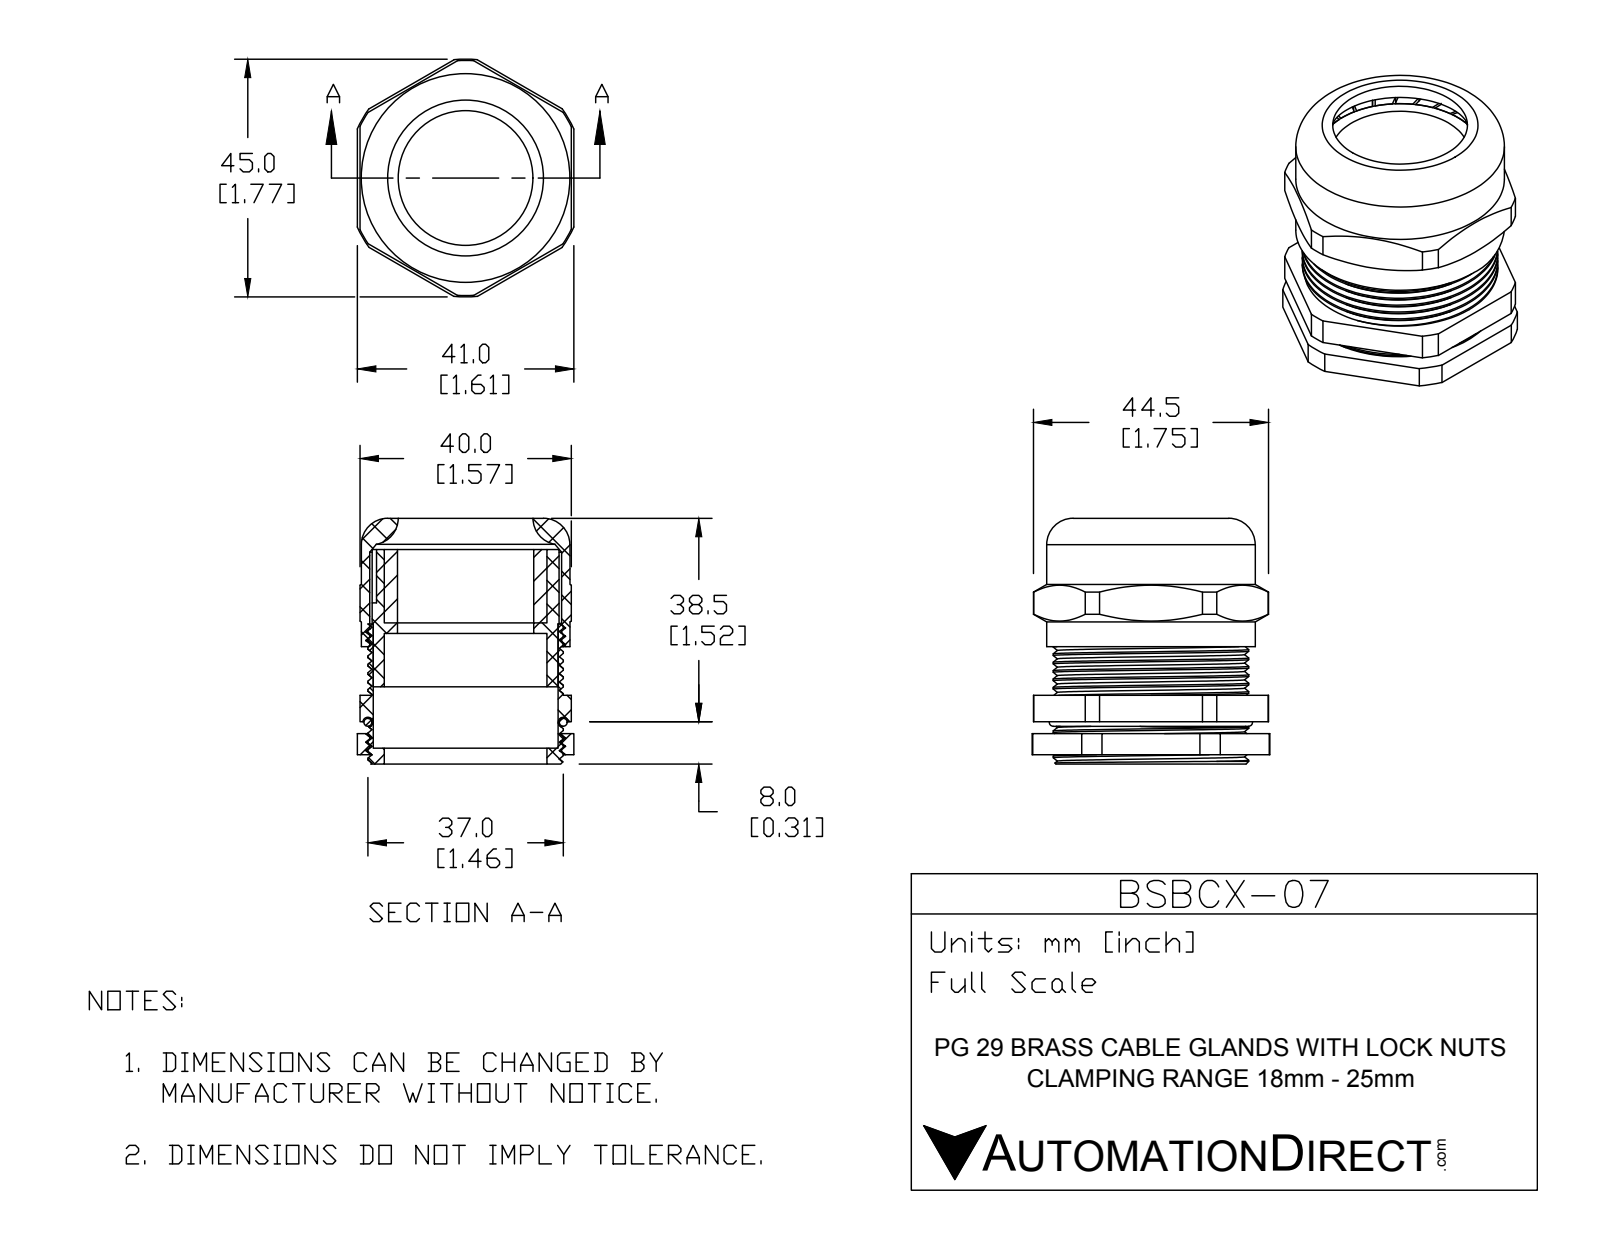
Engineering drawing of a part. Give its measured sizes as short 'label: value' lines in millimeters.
name: BSBCX-07
written by: SolidWorks 2015 (CONFIG_CONTROL_DESIGN)
unit: mm
bodies: 6 solids, 246 faces (134 planar, 82 cylindrical, 30 other)
size: 46.5 × 45 × 41
volume: 22 070 mm³; area: 28 124 mm²
holes: 1× ⌀25.8, 1× ⌀30.8, 1× ⌀35, 1× ⌀36.33
bosses: 1× ⌀39.5, 1× ⌀37, 1× ⌀35.4
rounds: 1× R22.25, 1× R22.5
face distances: 0.5, 40, 40.5, 13.9, 4, 5, 20.95, 34.85, 24.95, 38.85
